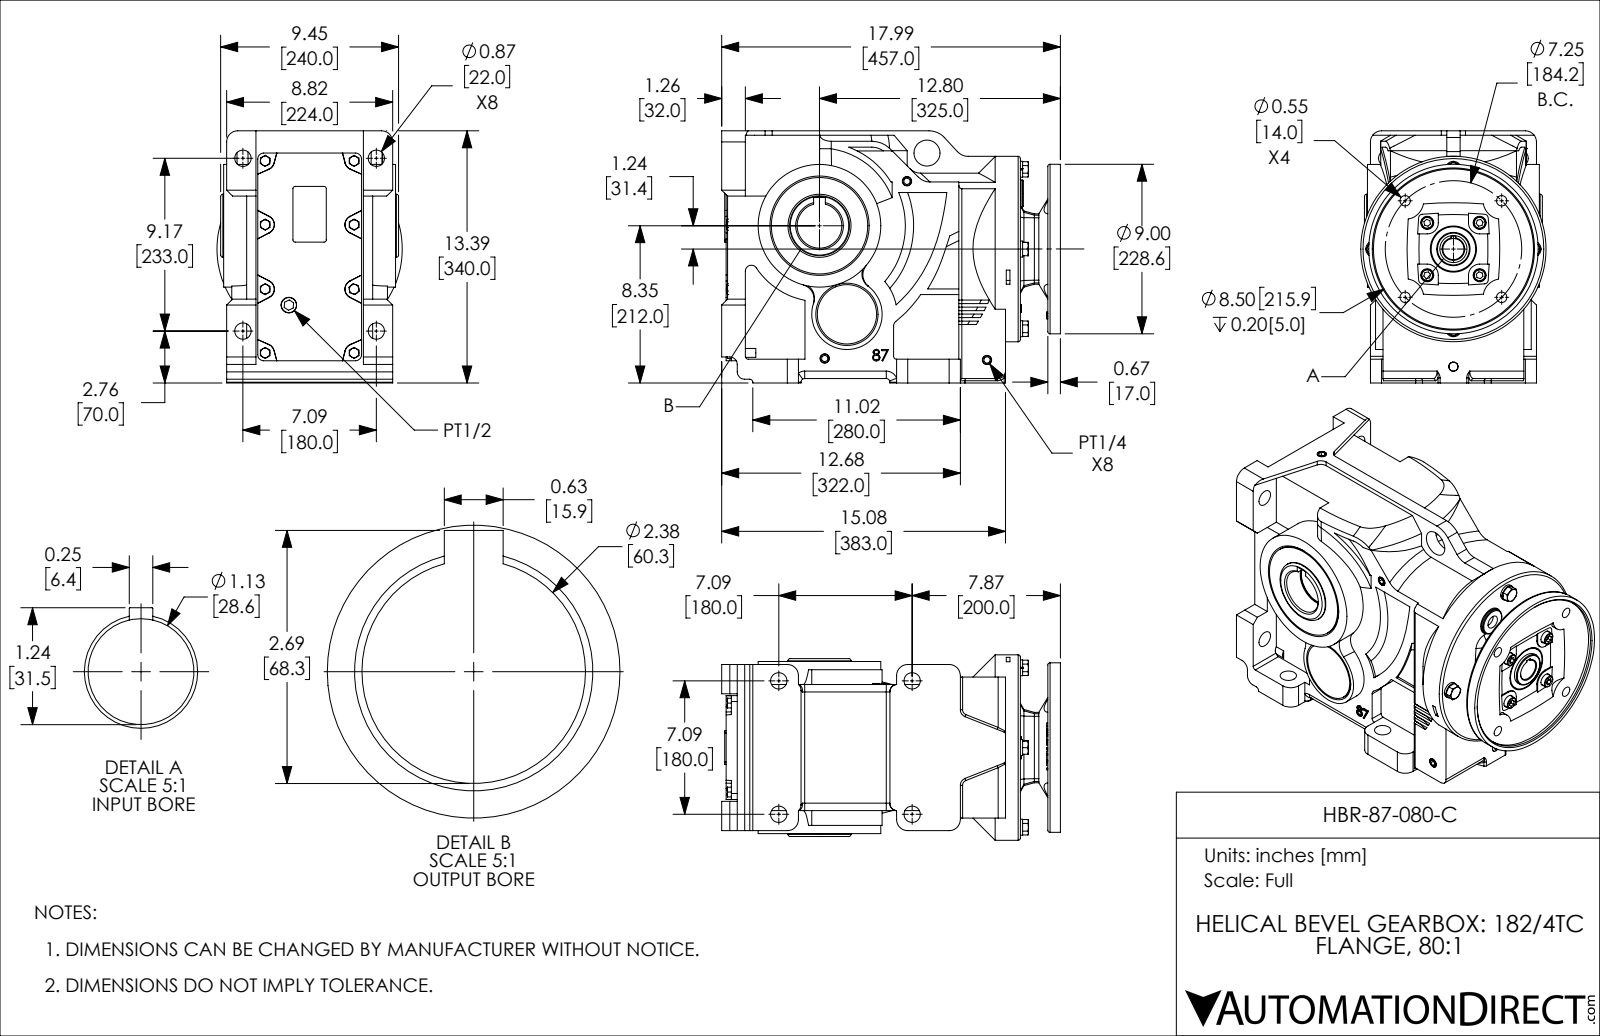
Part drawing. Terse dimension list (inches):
name: HBR-87-080-C
written by: SolidWorks 2018 (AUTOMOTIVE_DESIGN)
unit: in
bodies: 8 solids, 1111 faces (542 planar, 287 cylindrical, 282 other)
size: 17.992 × 13.501 × 9.843
volume: 1 396 in³; area: 1 309 in²
holes: 8× ⌀0.551, 8× ⌀0.866, 4× ⌀0.48, 4× ⌀0.496, 4× ⌀0.689, 1× ⌀0.473, 1× ⌀0.709, 1× ⌀0.827, 1× ⌀1.125, 1× ⌀1.378, 1× ⌀1.417, 1× ⌀2.375
bosses: 4× ⌀0.846, 4× ⌀0.63, 4× ⌀0.472, 1× ⌀9.843, 1× ⌀9, 1× ⌀6.513, 1× ⌀5.118, 1× ⌀3.346
rounds: 15× R0.394, 14× R0.591, 11× R0.157, 9× R0.118, 6× R0.315, 4× R0.689, 4× R0.984, 4× R19.528
face distances: 0.669, 0.236, 6.024, 1.063, 1.457, 7.087, 13.15, 0.394, 15.63, 1.22
hole spacings: 3.163, 7.087, 7.263, 2.784, 3.059, 4.125, 4.125, 4.232
